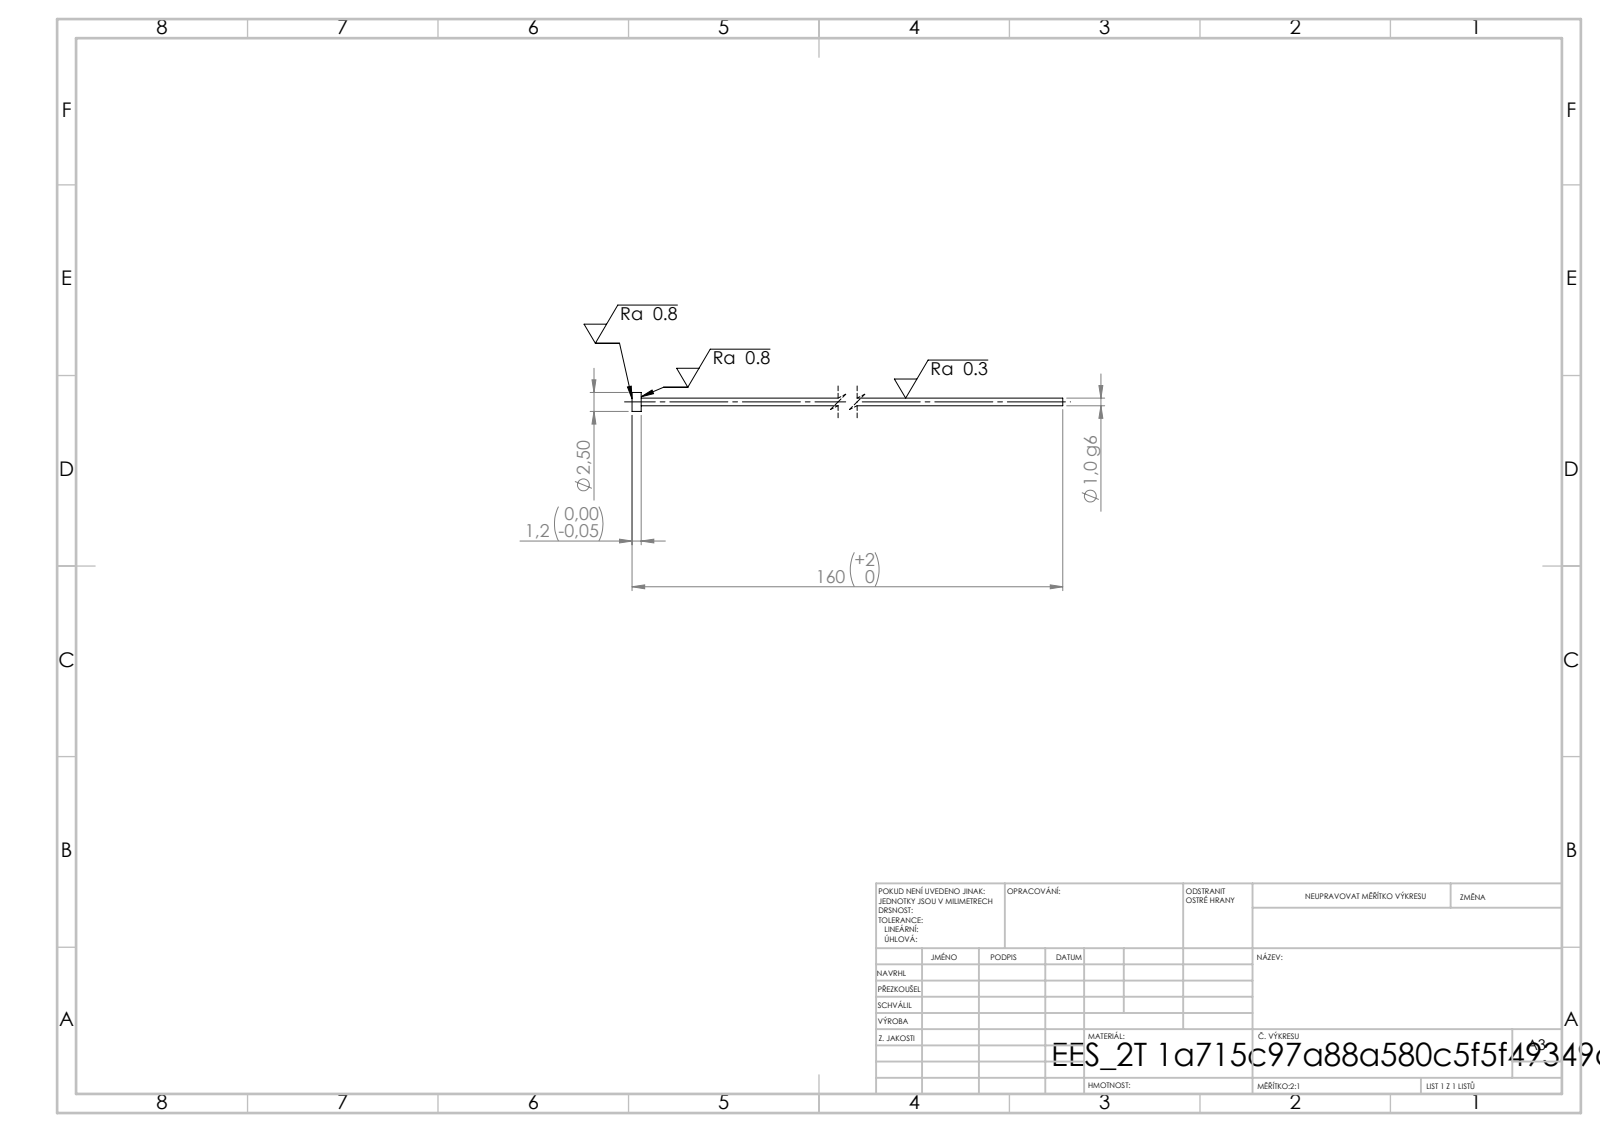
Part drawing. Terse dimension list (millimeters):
written by: SolidWorks 2019 (CONFIG_CONTROL_DESIGN)
unit: mm
bodies: 1 solid, 7 faces (3 planar, 4 cylindrical, 0 other)
size: 159.9 × 2.5 × 2.5
volume: 131 mm³; area: 518 mm²
bosses: 1× ⌀2.5, 1× ⌀1
face distances: 1.2, 159.9, 158.7
